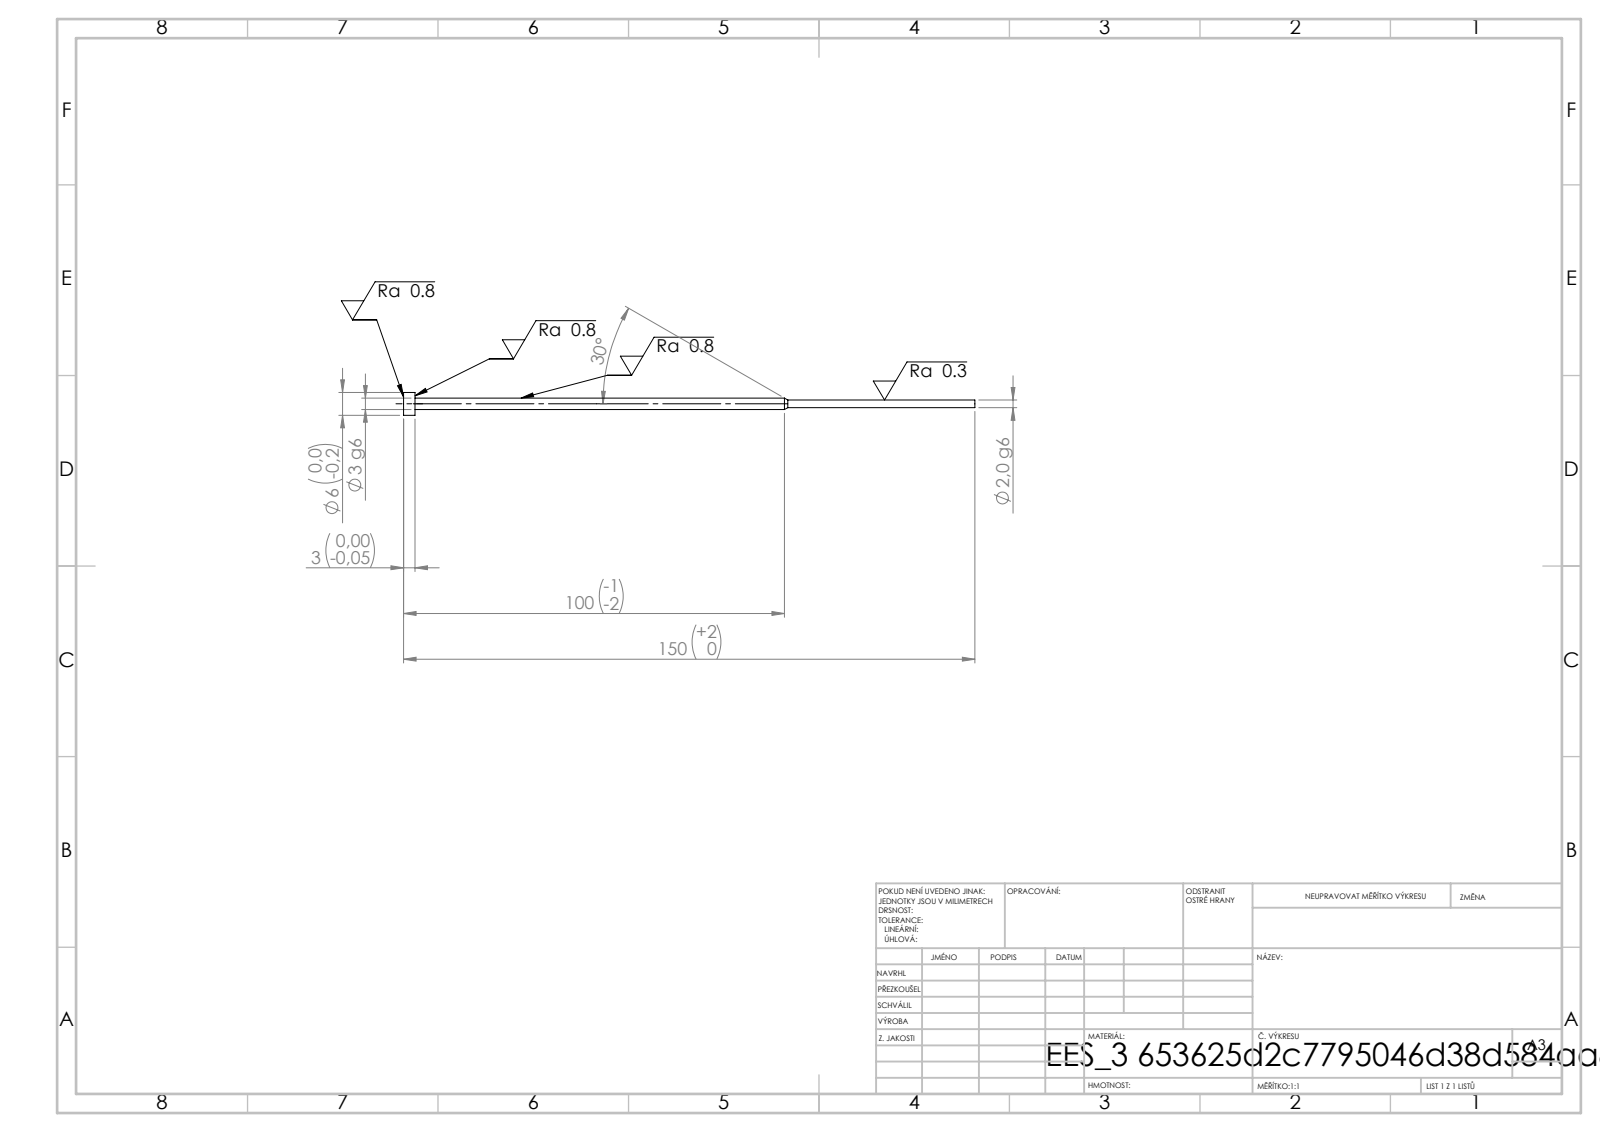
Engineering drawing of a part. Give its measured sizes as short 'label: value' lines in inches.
written by: SolidWorks 2019 (CONFIG_CONTROL_DESIGN)
unit: in
bodies: 1 solid, 11 faces (3 planar, 6 cylindrical, 2 other)
size: 5.906 × 0.236 × 0.236
volume: 0.057 in³; area: 2.077 in²
bosses: 1× ⌀0.236, 1× ⌀0.118, 1× ⌀0.079
face distances: 0.118, 5.787, 5.906
